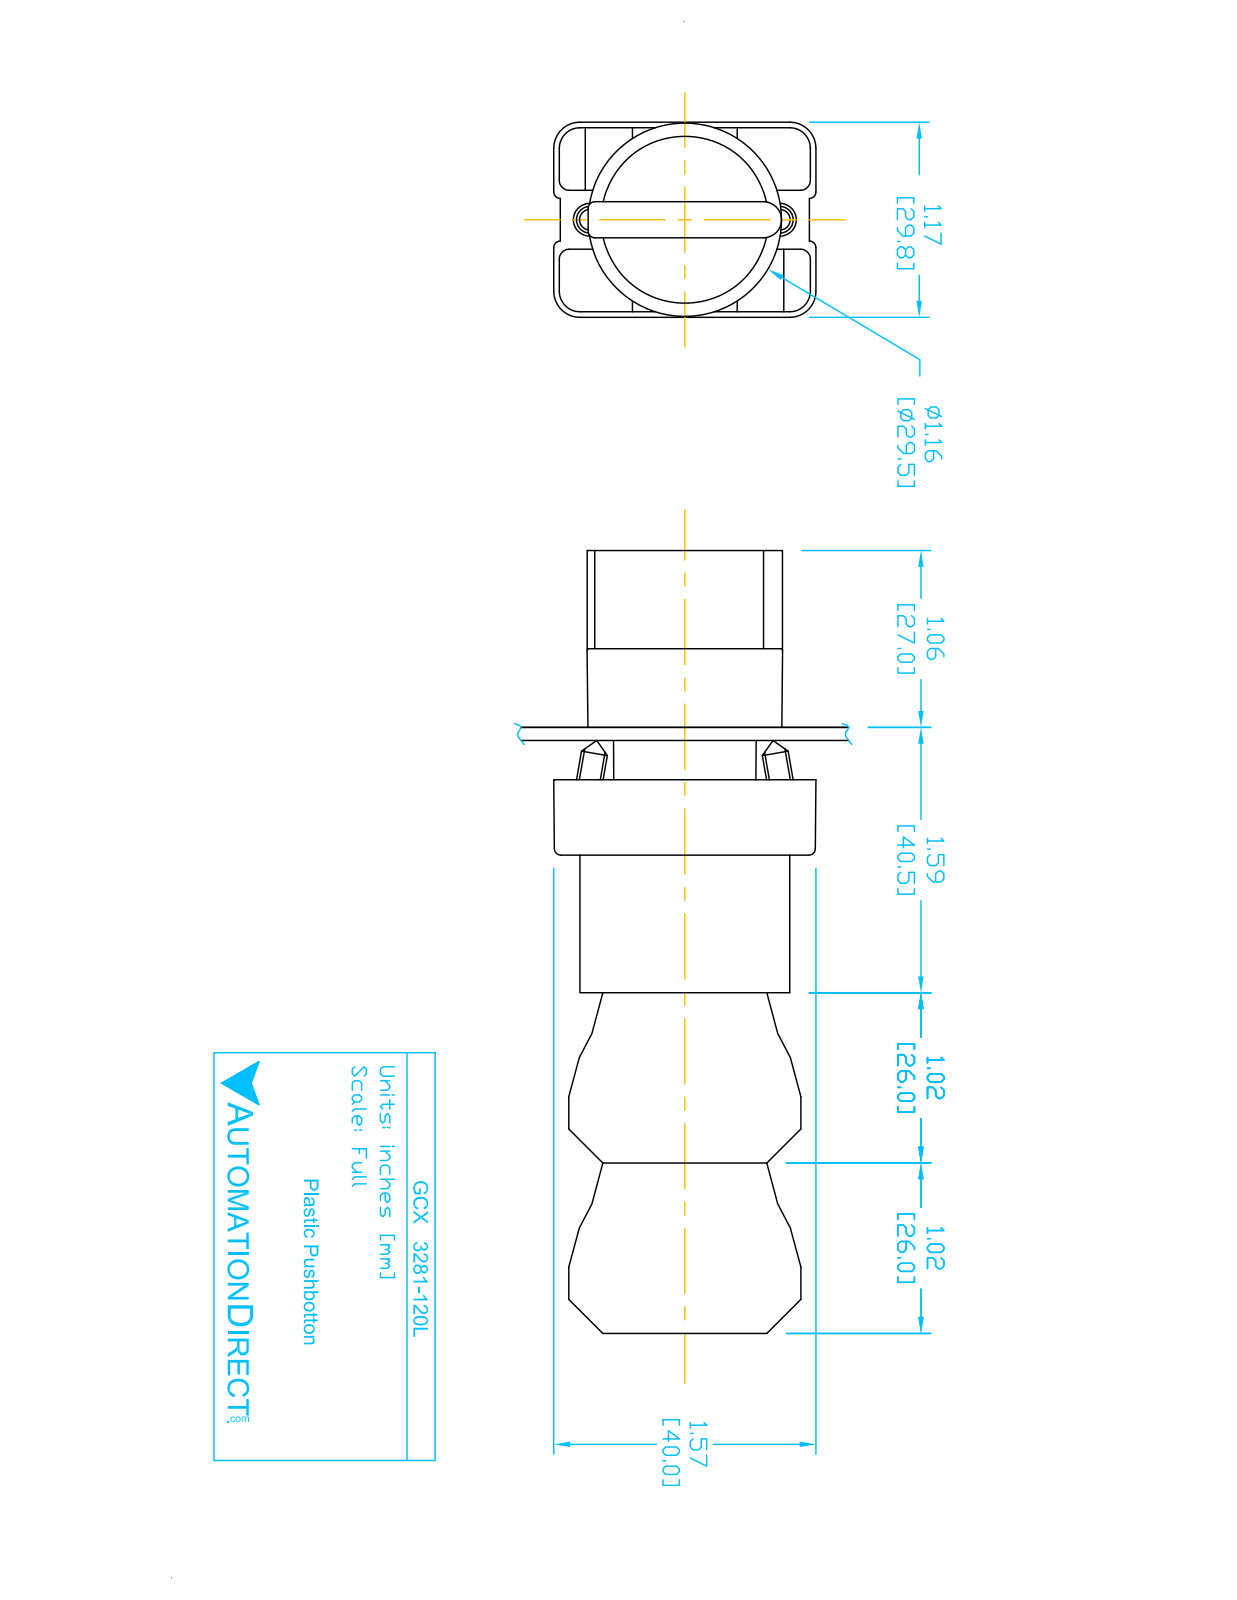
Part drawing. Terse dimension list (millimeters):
name: ECX1050; GCX3281L OPERATOR; ECX3029-2; ecx1040 (+2 more)
written by: SolidWorks 2016 (AUTOMOTIVE_DESIGN)
unit: mm
bodies: 11 solids, 724 faces (488 planar, 193 cylindrical, 43 other)
size: 118.8 × 40.2 × 29.9
volume: 77 850 mm³; area: 38 210 mm²
holes: 4× ⌀2, 2× ⌀2.2, 2× ⌀3.1, 2× ⌀3.3, 1× ⌀5, 1× ⌀11.9, 1× ⌀22.3, 1× ⌀22.6, 1× ⌀26
bosses: 4× ⌀4, 1× ⌀29.8, 1× ⌀25.5, 1× ⌀24, 1× ⌀21.7, 1× ⌀19.8, 1× ⌀12.8
rounds: 24× R1.5, 12× R1, 12× R3.1, 12× R4, 9× R1, 2× R0.5, 2× R1.6, 2× R2
face distances: 14.7, 15.1, 26, 29.7, 0.4, 21, 47, 77.3, 51.3, 30.3
hole spacings: 6, 25.5, 24.7, 12, 13.7, 13.8, 27.5, 12.3
